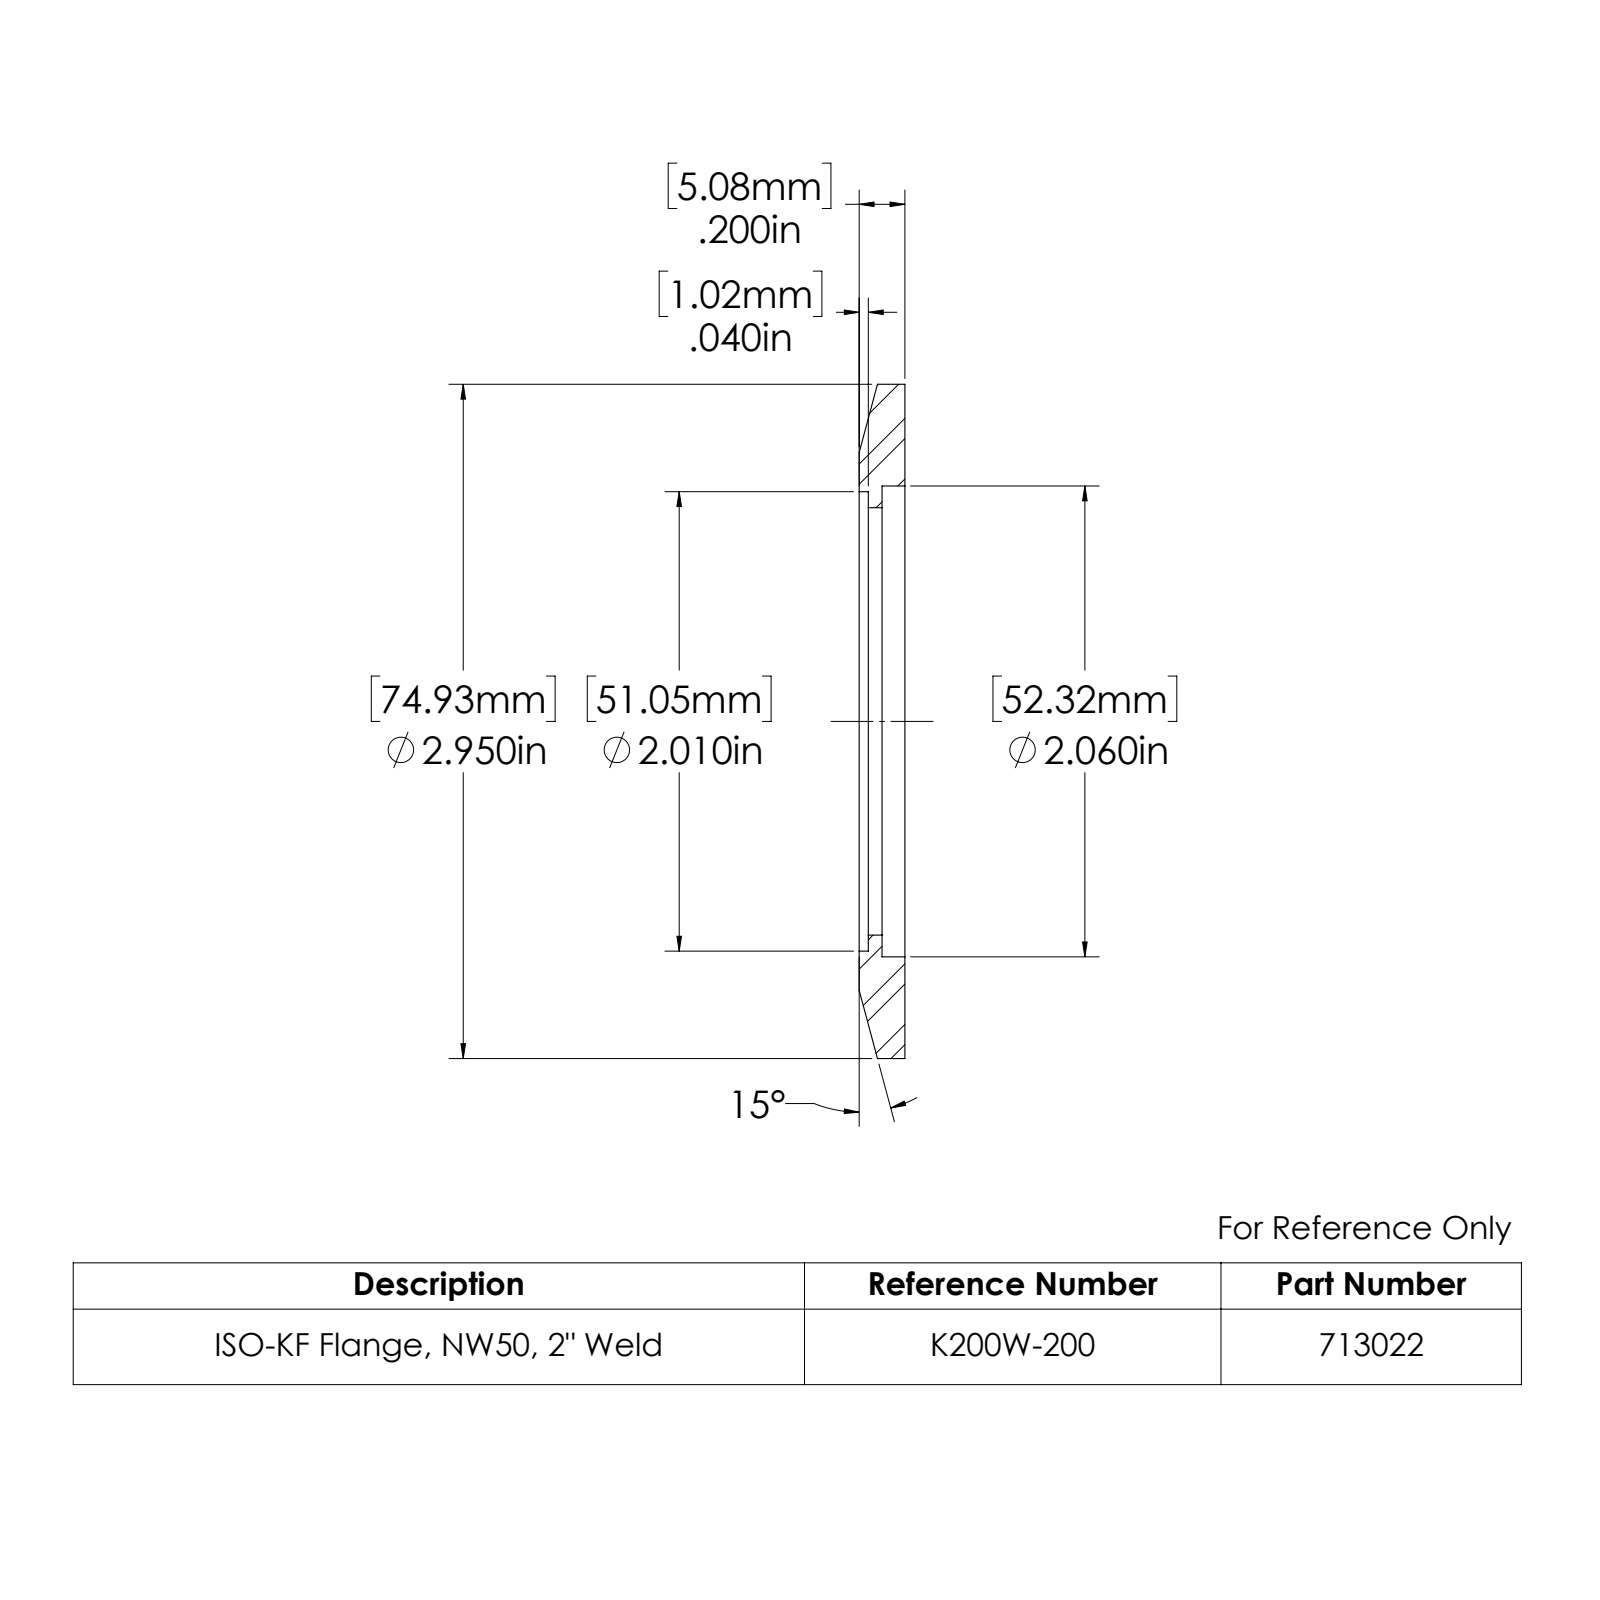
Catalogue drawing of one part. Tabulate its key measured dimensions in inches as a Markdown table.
| quantity | value |
| --- | --- |
| part name | 713022-REV.F |
| STEP written by | SolidWorks 2022 (AUTOMOTIVE_DESIGN) |
| units | inches |
| bodies | 1 solid, 14 faces (4 planar, 8 cylindrical, 2 other) |
| overall size | 2.95 × 2.95 × 0.2 |
| volume | 0.63 in³ |
| surface area | 10.64 in² |
| round holes (diameter × count) | 1.87 × 1, 2.01 × 1, 2.06 × 1 |
| round bosses / shafts (diameter × count) | 2.95 × 1 |
| main face-to-face distances | 0.2, 0.1, 0.14, 0.04, 0.06 |
